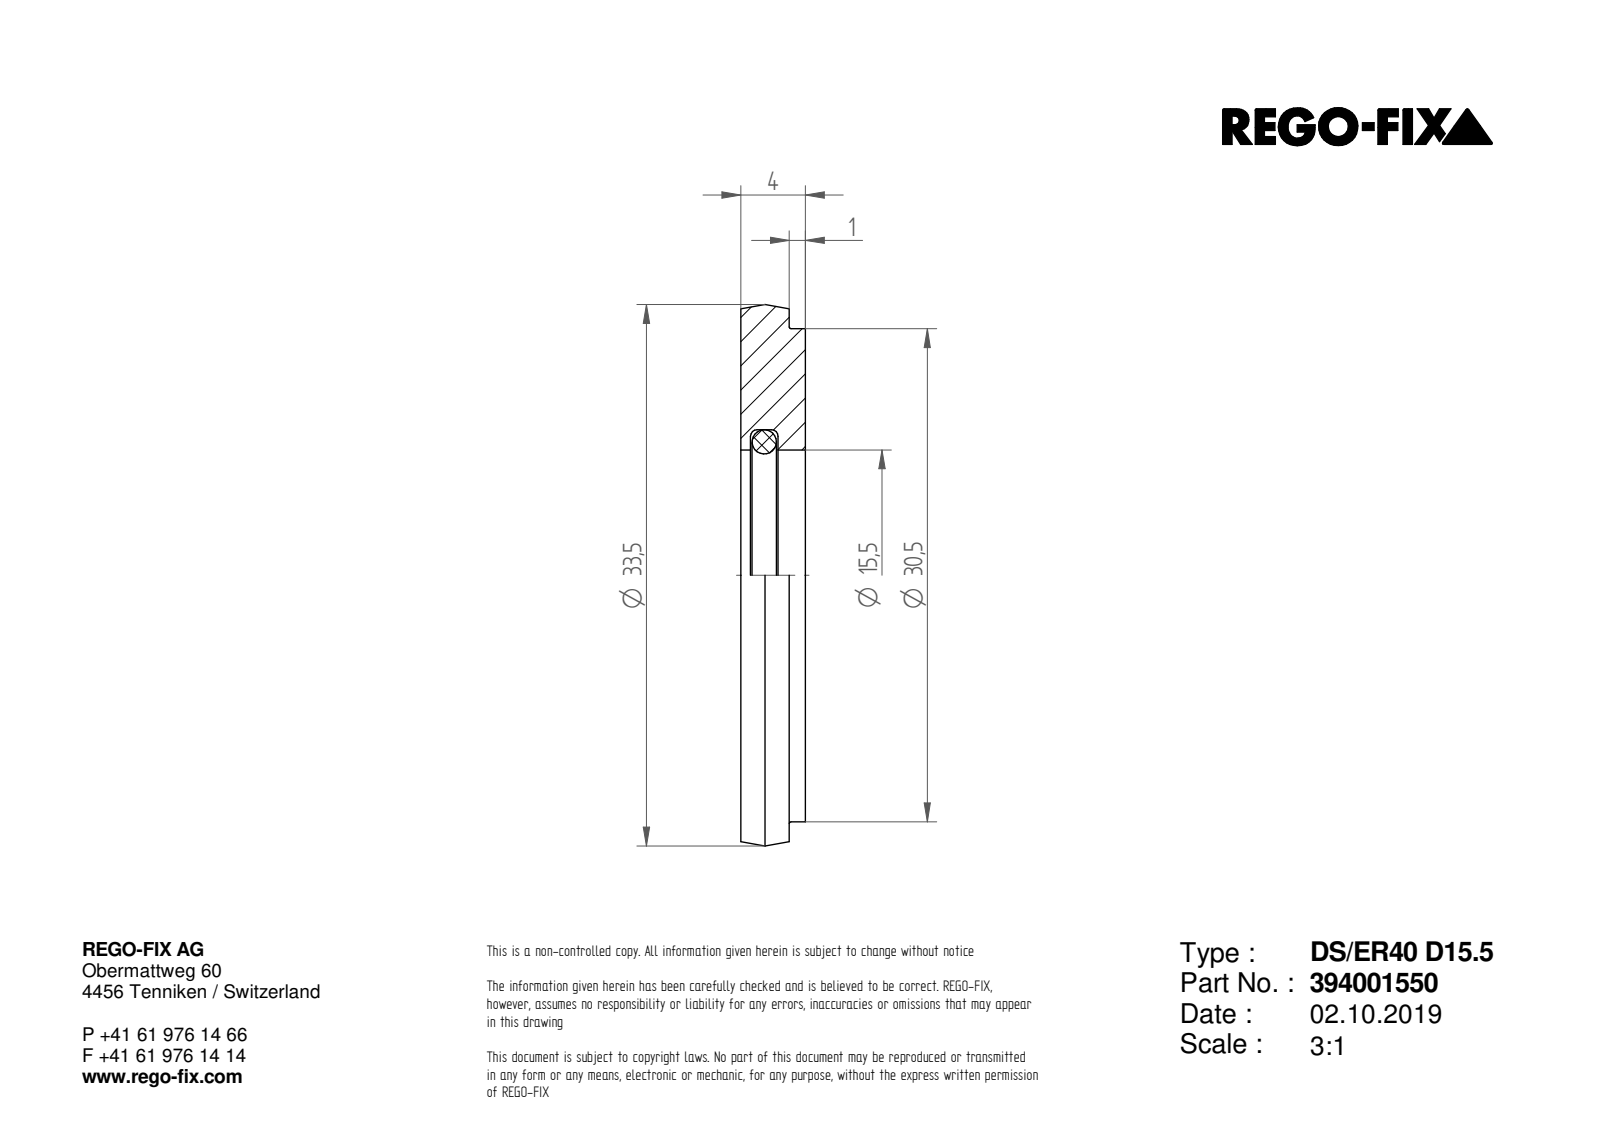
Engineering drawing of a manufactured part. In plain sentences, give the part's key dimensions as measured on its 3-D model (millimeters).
The part is named "NOCUT". Its 3-D file was written by "SIEMENS PLM Software Solid Edge ST10 (AUTOMOTIVE_DESIGN)". It is 1 solid with 7 faces: 3 planar, 3 cylindrical and 1 other. Overall it measures 33.5 by 33.5 by 4 millimeters. Its volume is 2 620 cubic millimeters and its surface area 1 988 square millimeters. Round holes: 1 of diameter 15.5. Round bosses or shafts: 1 of diameter 33.5, 1 of diameter 30.5. The main face-to-face distances are 4, 1, 3.
